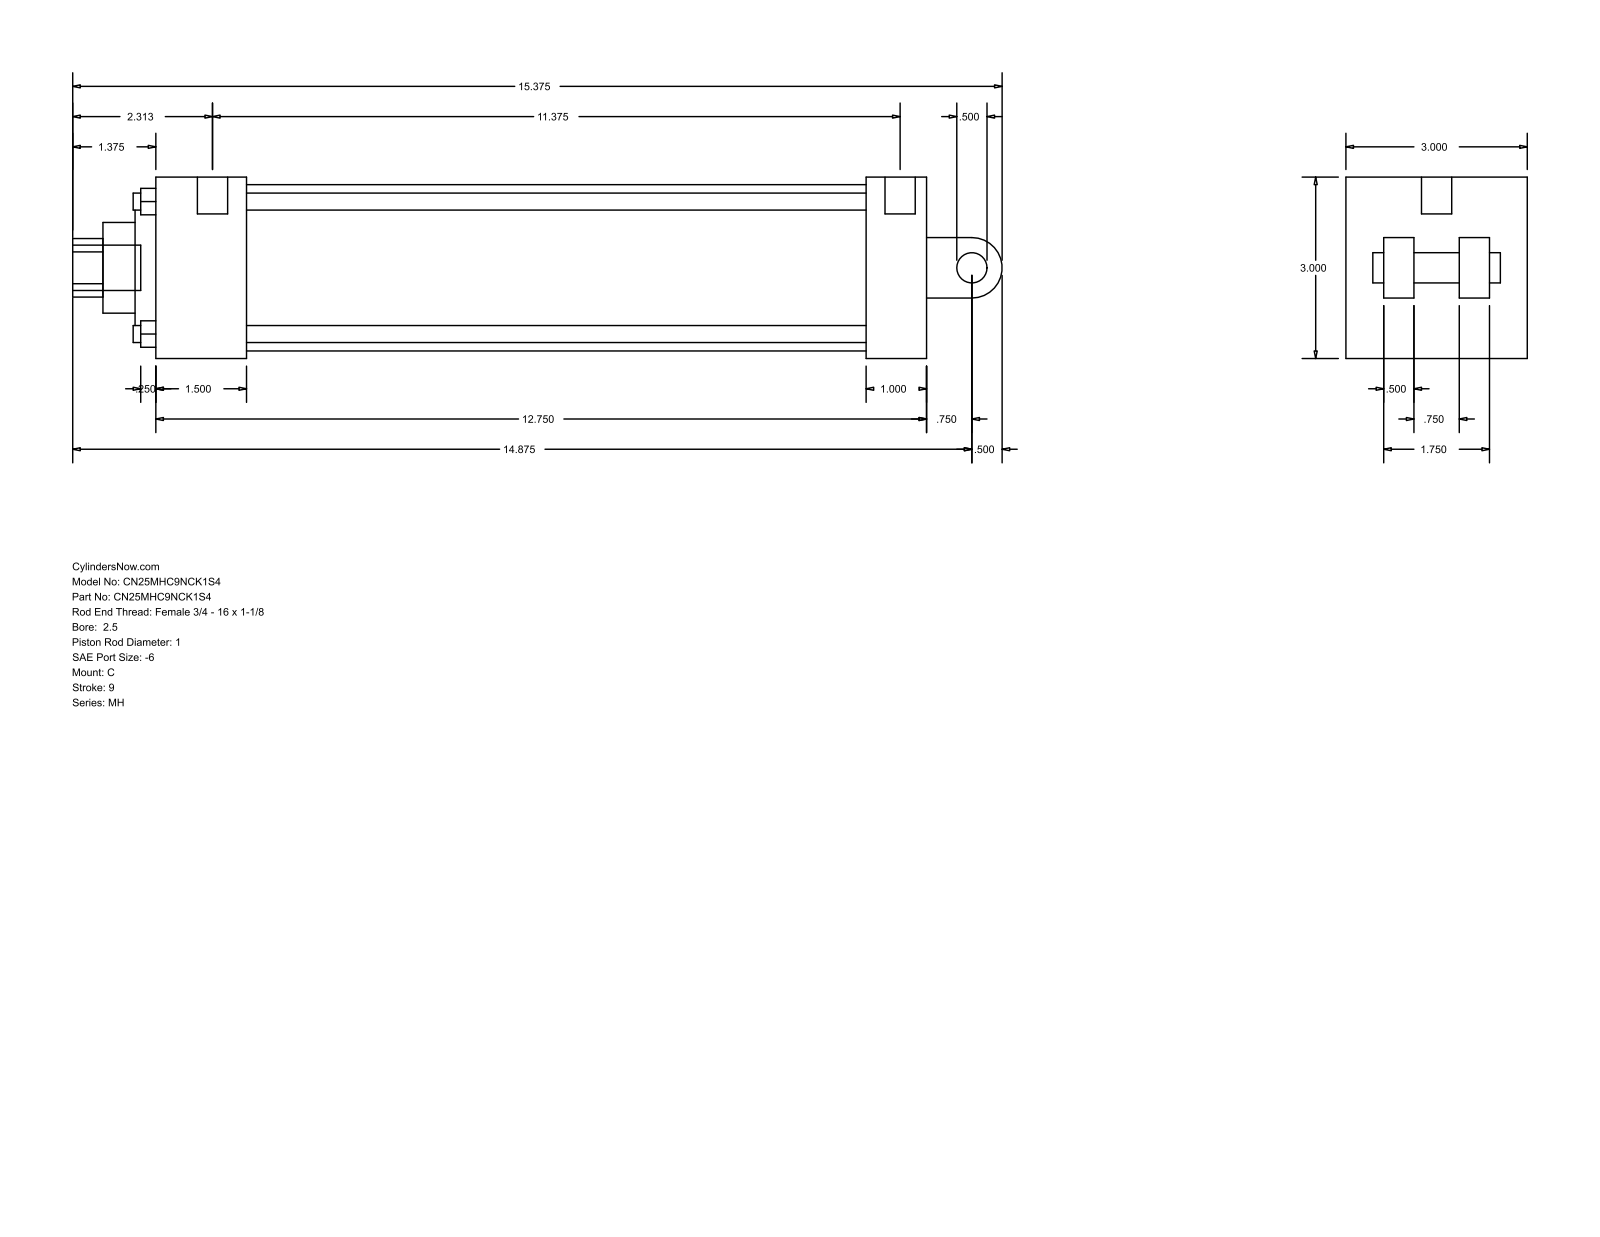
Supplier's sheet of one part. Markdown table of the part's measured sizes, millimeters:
| quantity | value |
| --- | --- |
| part name | MH_C__0250_1 |
| STEP written by | GSSL Pune (CONFIG_CONTROL_DESIGN) |
| units | millimeters |
| bodies | 0 solids, 101 faces (71 planar, 30 cylindrical, 0 other) |
| overall size | 390.52 × 76.2 × 76.2 |
| round holes (diameter × count) | 7.14 × 4, 5.56 × 2, 12.7 × 1, 25.4 × 1, 38.1 × 1, 60.33 × 1, 69.85 × 1 |
| round bosses / shafts (diameter × count) | 12.7 × 2, 5.56 × 2, 19.05 × 1 |
| partial cylindrical surfaces (radius × count) | 12.29 × 1, 12.7 × 1 |
| main face-to-face distances | 76.2, 323.85, 15.87, 25.39, 60.33, 298.46, 38.11, 260.35, 285.74, 12.7 |
| hole center spacings | 39.33, 55.62, 78.66, 3.18 |
